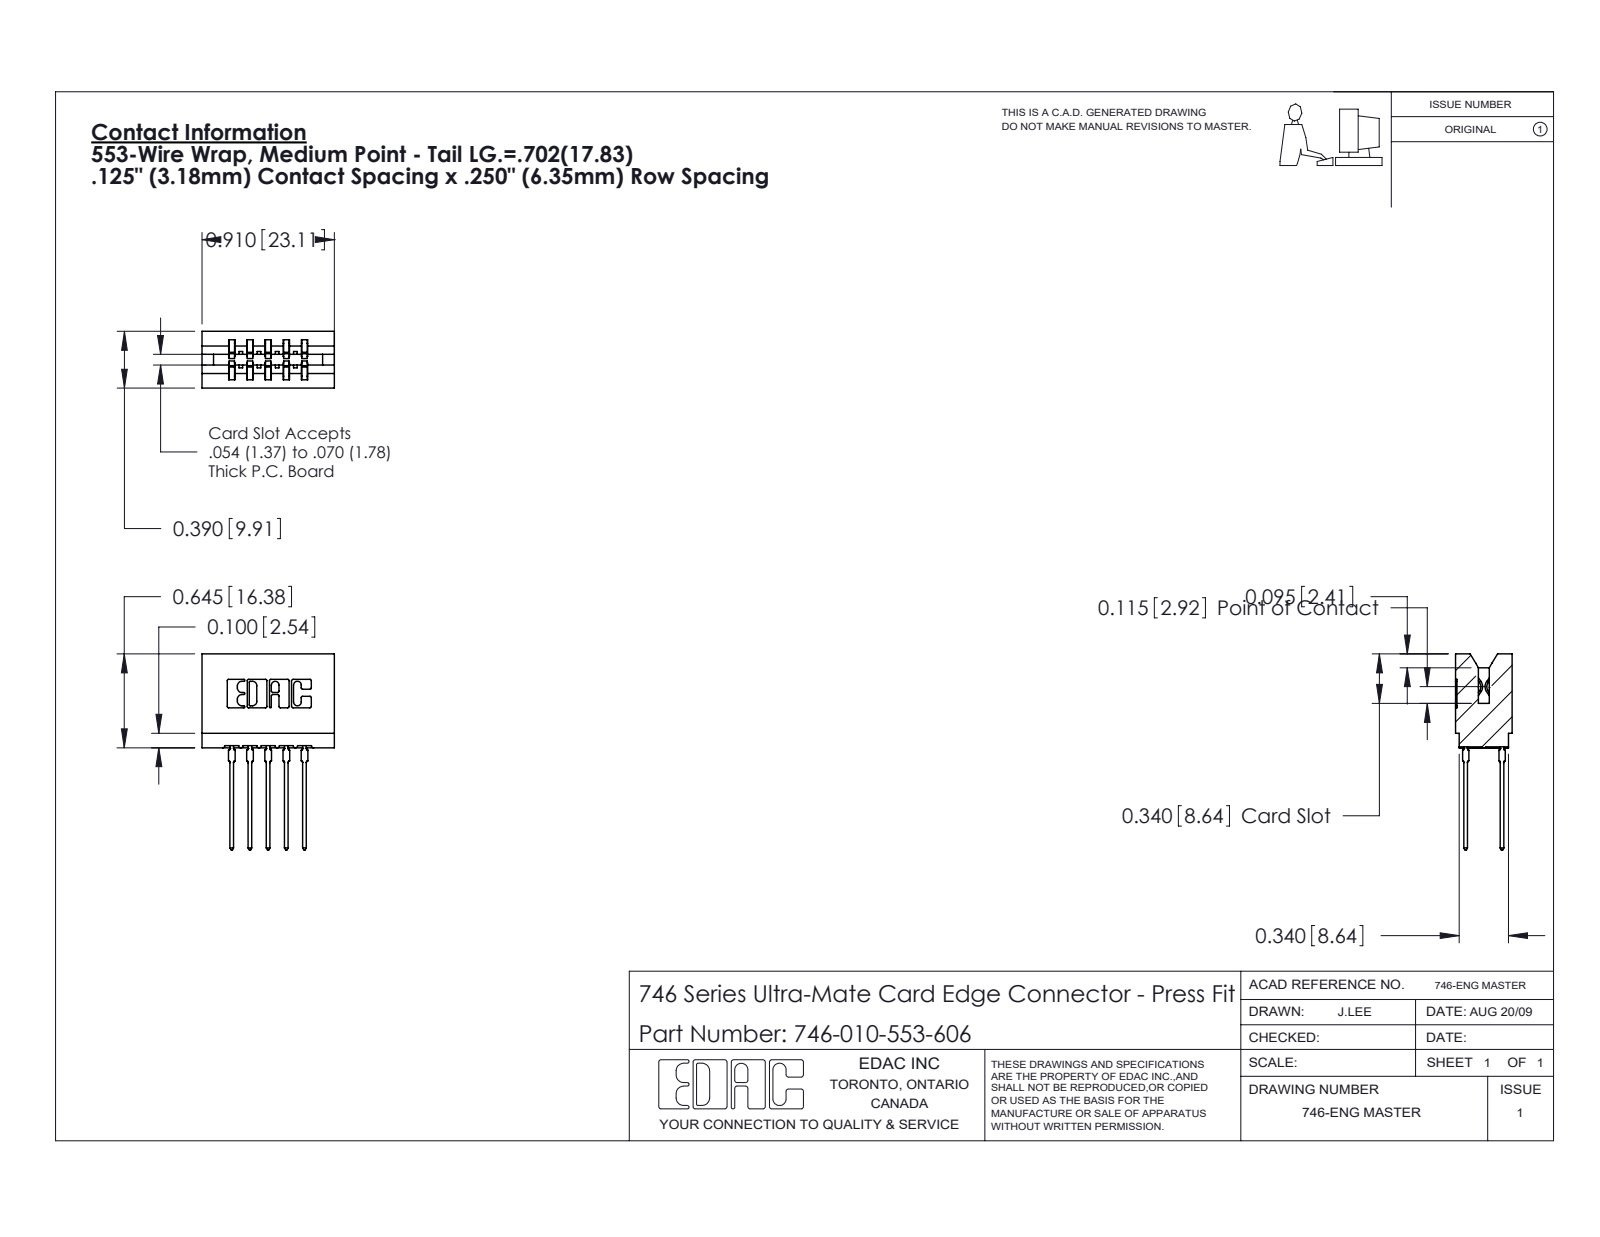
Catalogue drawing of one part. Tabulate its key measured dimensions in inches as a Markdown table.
| quantity | value |
| --- | --- |
| part name | 746-292-001_553; 746 Part_.340 Slot Depth - 06; 746-010-553-606 |
| STEP written by | SolidWorks 2020 (CONFIG_CONTROL_DESIGN) |
| units | inches |
| bodies | 11 solids, 993 faces (516 planar, 217 cylindrical, 260 other) |
| overall size | 1.346 × 0.91 × 0.39 |
| volume | 0.176 in³ |
| surface area | 5.864 in² |
| partial cylindrical surfaces (radius × count) | 0.01 × 22, 0.021 × 20, 0.005 × 8, 0.011 × 8, 0.007 × 6, 0.015 × 6, 0.031 × 6, 0.026 × 3 |
| main face-to-face distances | 0.25, 0.057, 0.333, 0.042, 0.125, 0.125, 0.083, 0.025, 0.39, 0.307 |
